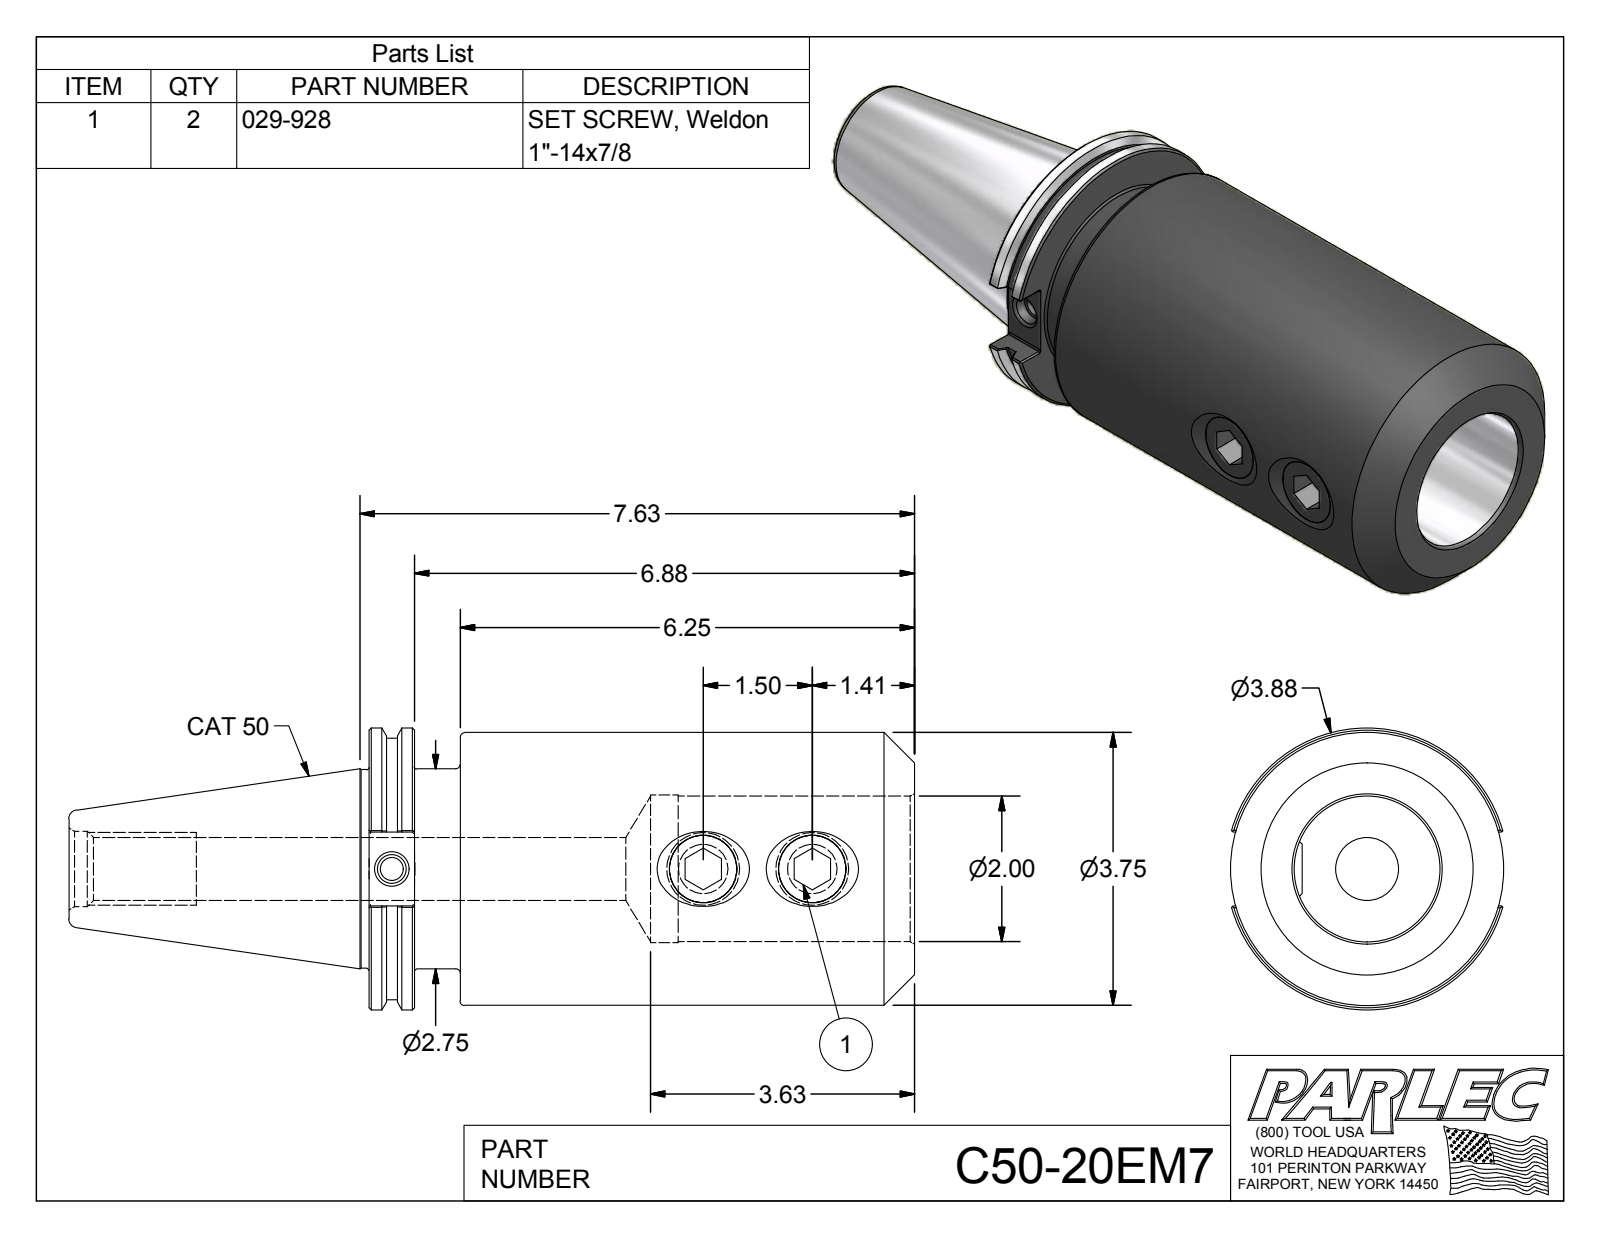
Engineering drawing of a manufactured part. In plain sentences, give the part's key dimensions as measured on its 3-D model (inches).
The part is named "C50-20EM7; C50-20EM7-1; 029-928". Its 3-D file was written by "Autodesk Inventor 2012 (AUTOMOTIVE_DESIGN)". It is 3 solids with 119 faces: 52 planar, 31 cylindrical and 36 other. Overall it measures 11.625 by 3.875 by 3.75 inches. Its volume is 77.26 cubic inches and its surface area 196.4 square inches. Round holes: 2 of diameter 0.923, 1 of diameter 0.315, 1 of diameter 0.399, 1 of diameter 0.865, 1 of diameter 1.038, 1 of diameter 2, 1 of diameter 2.03. Round bosses or shafts: 2 of diameter 1, 1 of diameter 3.875, 1 of diameter 3.75, 1 of diameter 3.594, 1 of diameter 2.75, 1 of diameter 2.73. Partial cylindrical surfaces (rounded edges, fillets, slot ends): 12 of radius 0.02. The main face-to-face distances are 0.625, 1.255, 0.63, 7.5, 6.875, 6.245, 0.5, 0.875, 2.284, 3.159. The hole center spacings are 1.5, 4.279, 5.779.
